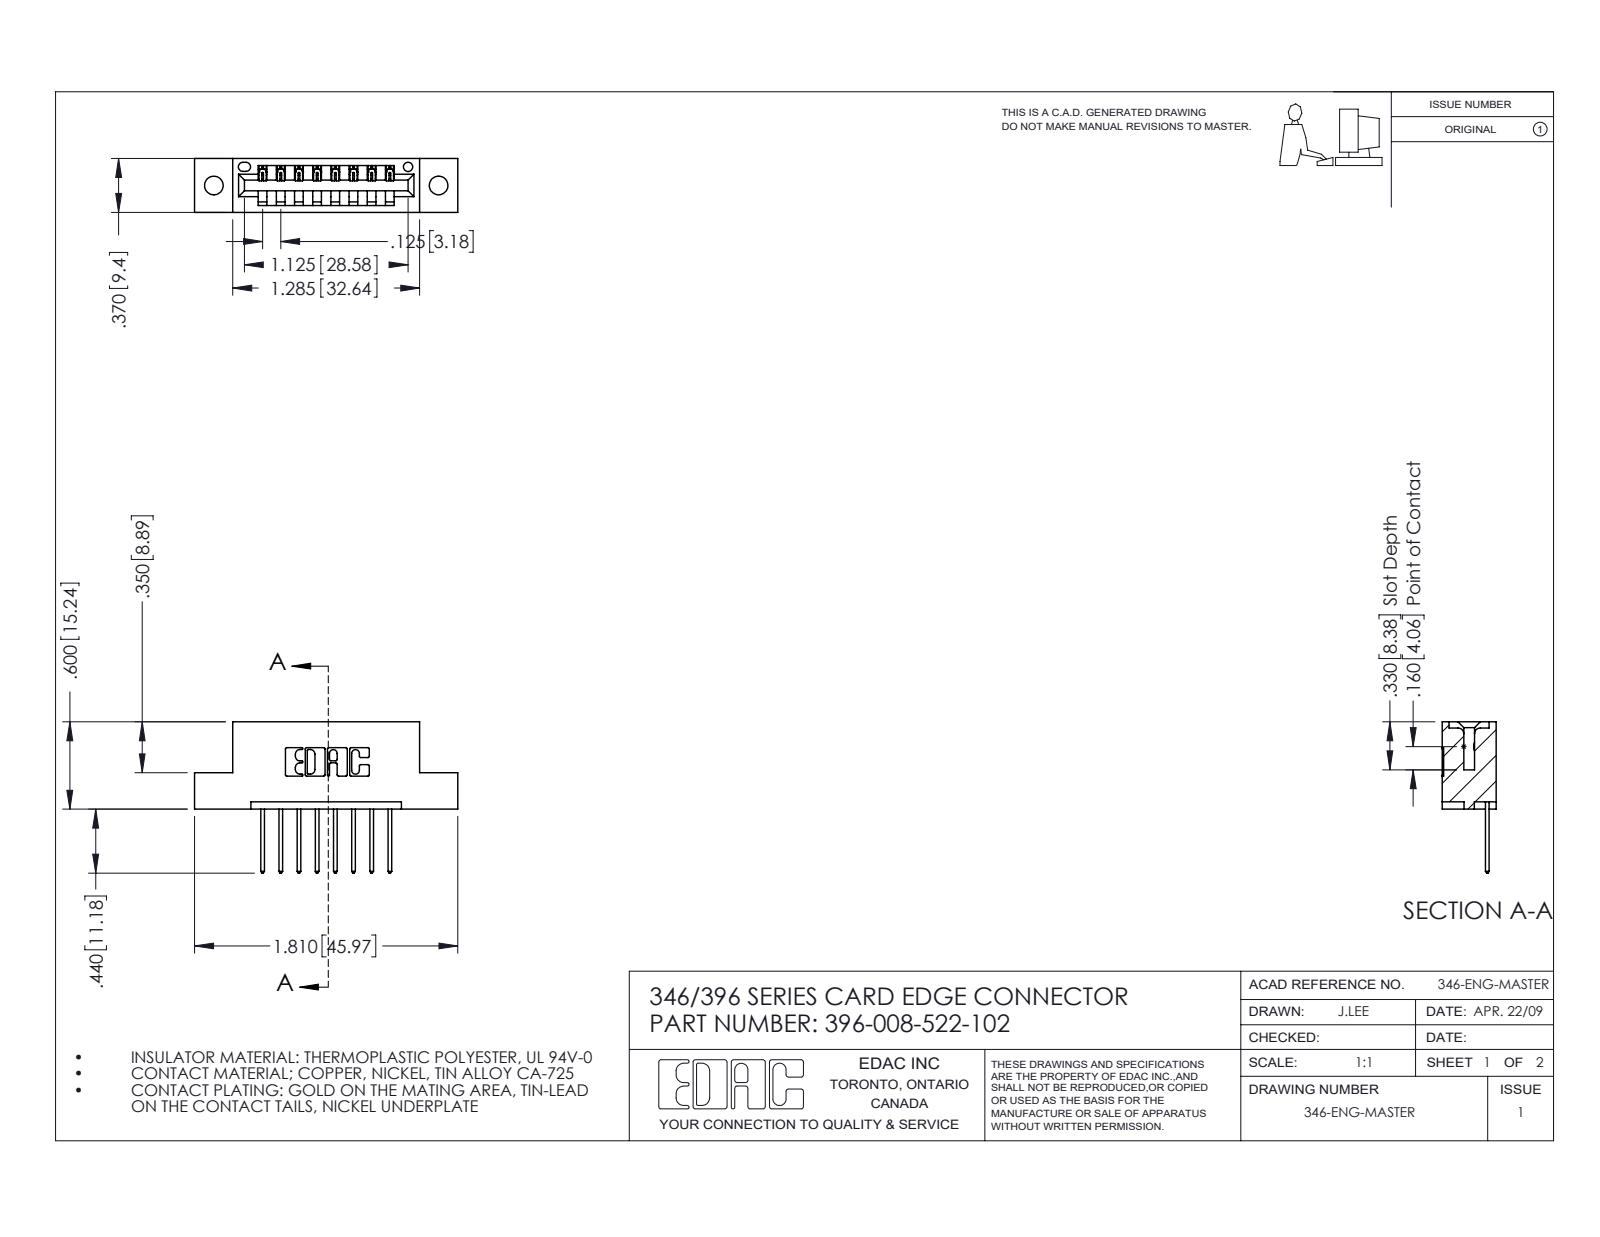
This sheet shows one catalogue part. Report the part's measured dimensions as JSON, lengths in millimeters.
{"part_name": "396-008-522-102; 345-292-001_345-293-122; 346 Part_Flush Mounting Lugs - 0.128 Dia", "step_written_by": "SolidWorks 2016 (CONFIG_CONTROL_DESIGN)", "units": "millimeters", "bodies": {"solids": 9, "faces": 586, "planar": 396, "cylindrical": 190, "other": 0}, "overall_size": [46, 26.4, 9.4], "volume_mm3": 4130, "surface_area_mm2": 4554, "round_holes": [[3.3, 2], [1.6, 1]], "partial_cylinders_radius": [[0.3, 22], [0.2, 16], [0.3, 16], [0.2, 6], [0.8, 6], [0.7, 3], [0.8, 2], [1, 2]], "face_to_face_distances": [6.4, 9.4, 1.2, 8.2, 12.7, 1.8, 7.6, 0.6, 3.8, 5.6], "hole_center_spacings": [6.2, 34.1, 39.2]}
